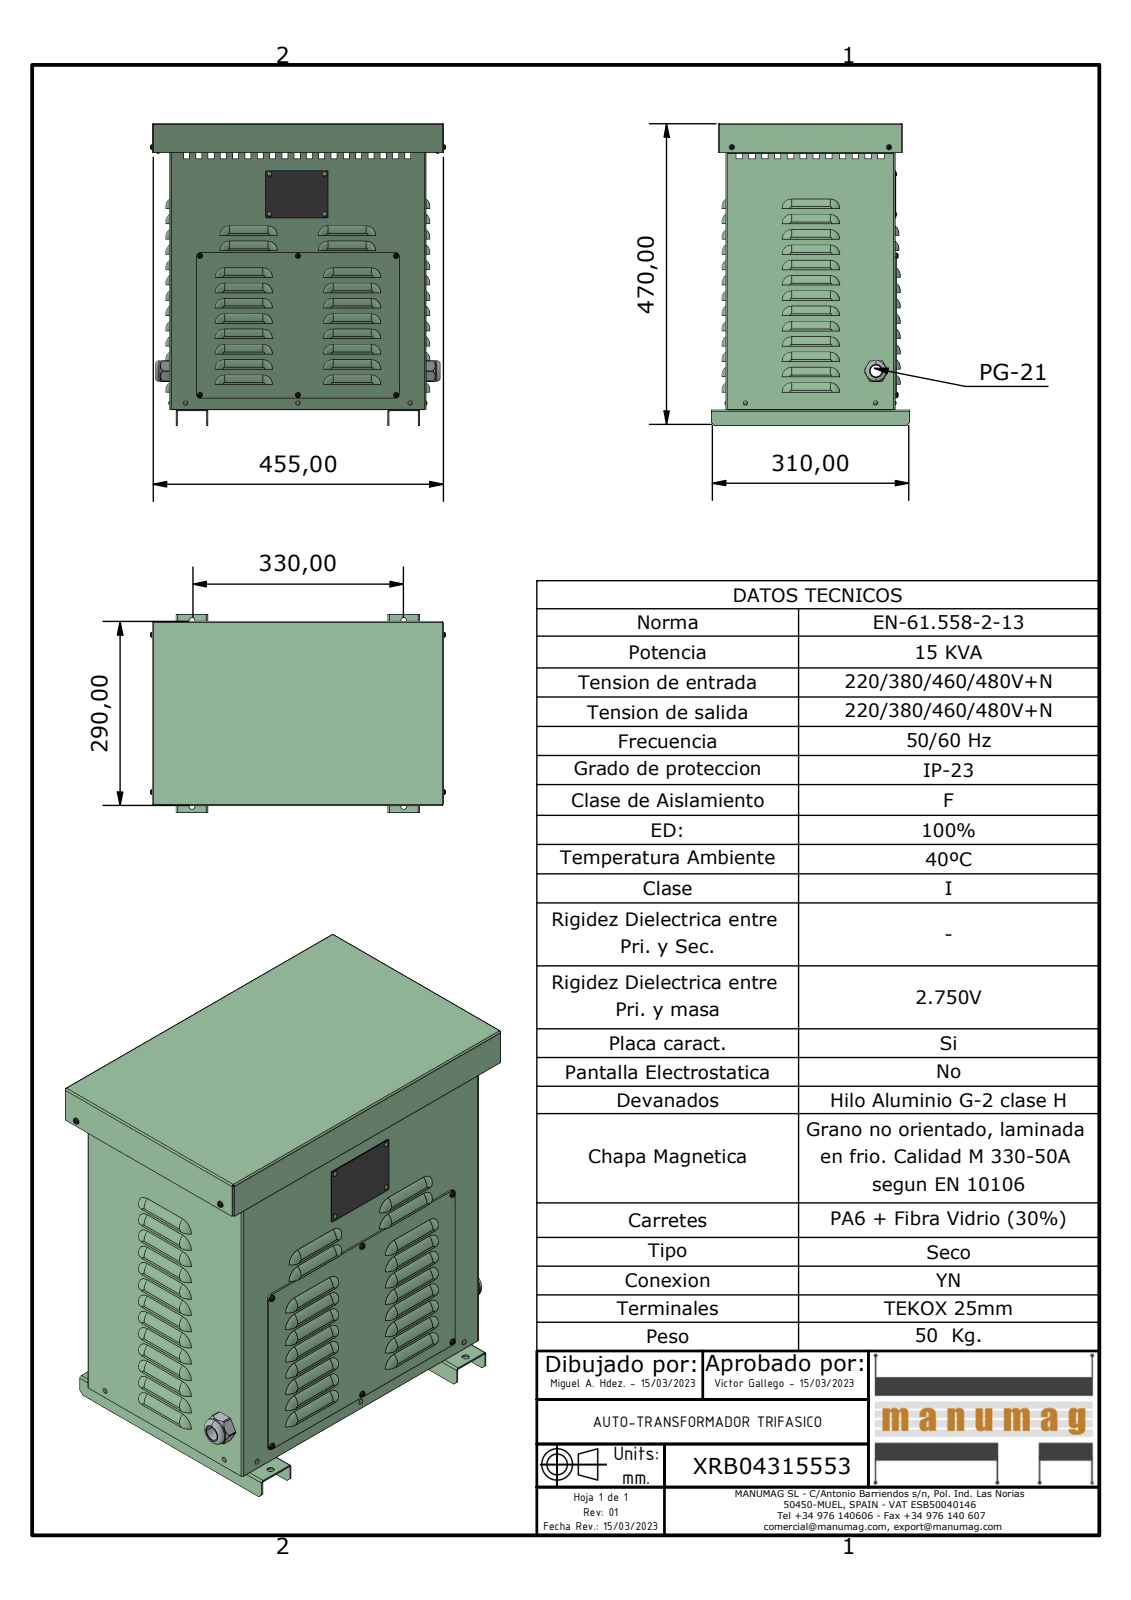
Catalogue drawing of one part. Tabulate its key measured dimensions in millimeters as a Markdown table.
| quantity | value |
| --- | --- |
| part name | XRB04315553; JE015 - JE020 - JE025 EXPORT CUERPO; JE015 - JE020 - JE025 EXPORT BASE; JE015 - JE020 - JE025 EXPORT PATA (+6 more) |
| STEP written by | Autodesk Inventor 2023 (AUTOMOTIVE_DESIGN) |
| units | millimeters |
| bodies | 33 solids, 2242 faces (1225 planar, 489 cylindrical, 528 other) |
| overall size | 474.44 × 463.69 × 310 |
| volume | 2 342 000 mm³ |
| surface area | 2 098 000 mm² |
| round holes (diameter × count) | 3.4 × 17, 4 × 9, 2.3 × 8, 9 × 6, 5.1 × 3, 8.92 × 2, 18 × 1, 29.9 × 1 |
| round bosses / shafts (diameter × count) | 3.2 × 9, 4 × 8, 3.62 × 8, 32.4 × 1, 28.5 × 1, 28.3 × 1 |
| partial cylindrical surfaces (radius × count) | 14 × 118, 4 × 63, 15 × 49, 2 × 10, 2 × 9, 3.47 × 8, 0.5 × 6, 2.5 × 6 |
| main face-to-face distances | 2, 262.92, 264.92, 400.8, 447.27, 449.27, 260.92, 398.8, 402.8, 4 |
| hole center spacings | 218.1, 153.8, 154.1, 266.87, 267.05, 307.9, 332.28, 377.32 |
